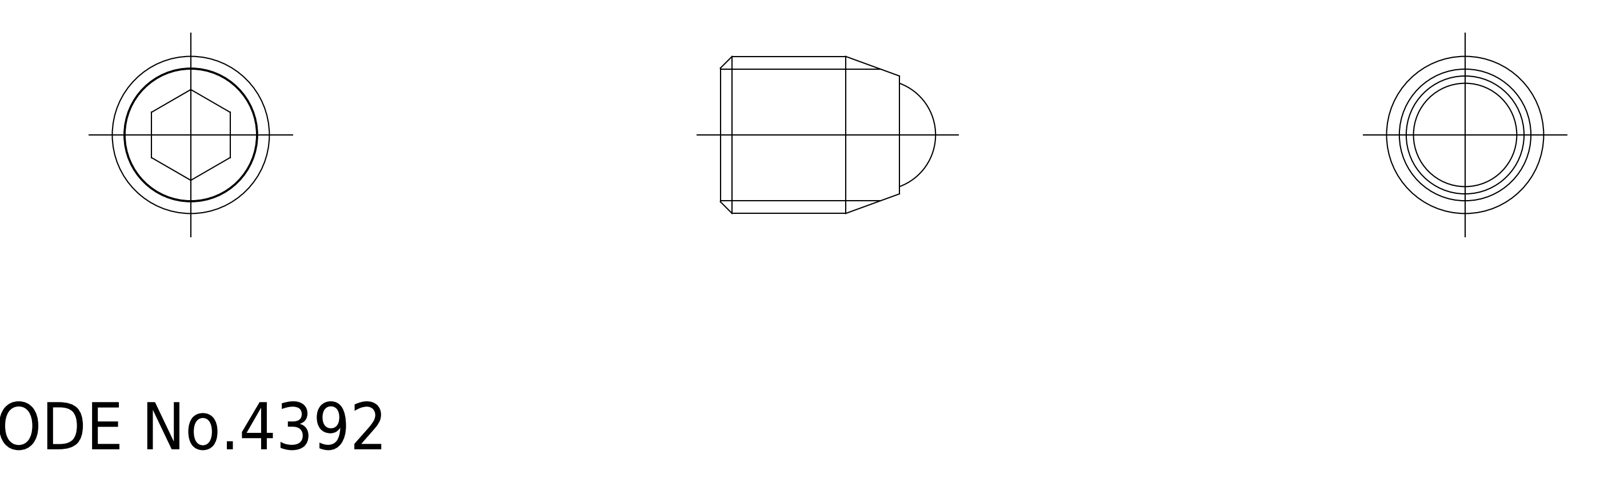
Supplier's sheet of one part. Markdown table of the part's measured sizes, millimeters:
| quantity | value |
| --- | --- |
| part name | ball; SCS_M10_12_R_15621_36 |
| STEP written by | CADfix (AUTOMOTIVE_DESIGN) |
| units | millimeters |
| bodies | 2 solids, 20 faces (0 planar, 0 cylindrical, 20 other) |
| overall size | 13.7 × 10 × 10 |
| volume | 685 mm³ |
| surface area | 827 mm² |
